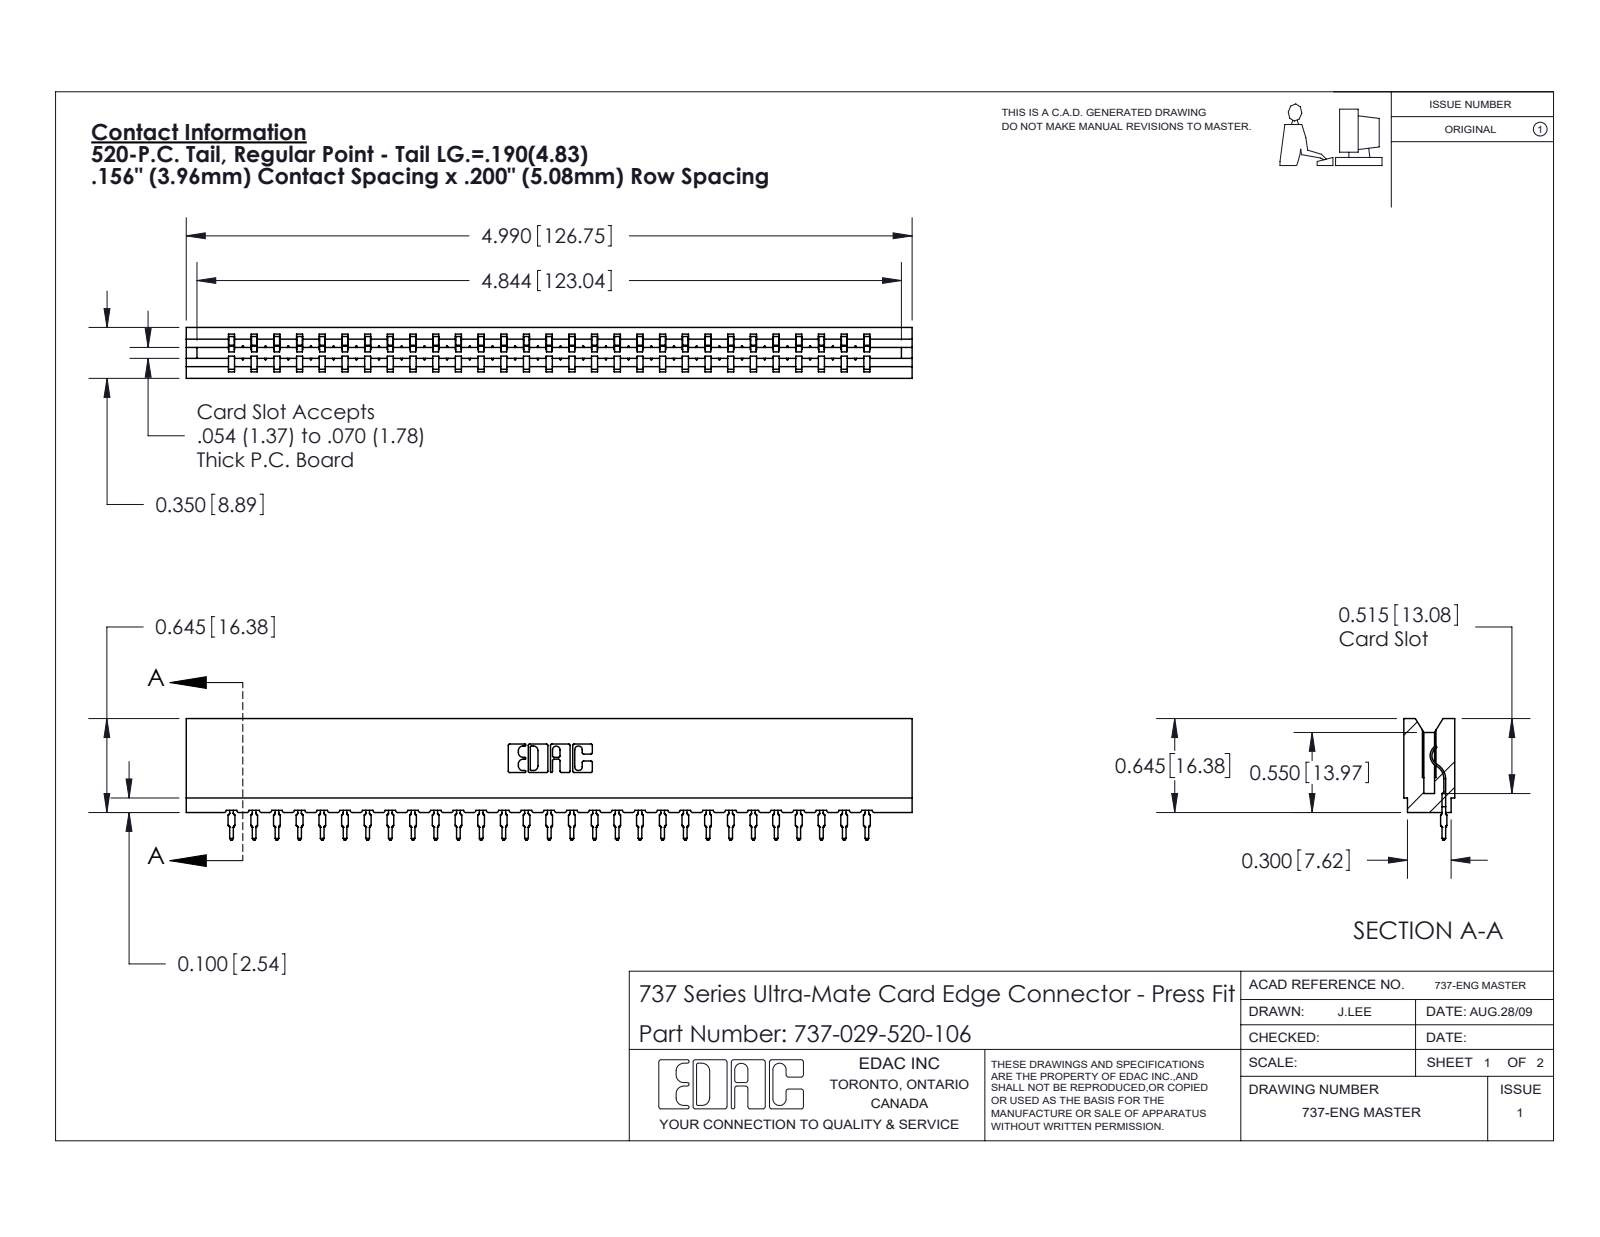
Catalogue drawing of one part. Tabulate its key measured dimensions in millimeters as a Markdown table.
| quantity | value |
| --- | --- |
| part name | 737 Part_Insulator Option - 06; 745-292-001_520; 737-029-520-106 |
| STEP written by | SolidWorks 2020 (CONFIG_CONTROL_DESIGN) |
| units | millimeters |
| bodies | 30 solids, 3372 faces (2027 planar, 591 cylindrical, 754 other) |
| overall size | 126.7 × 21.2 × 8.9 |
| volume | 12 300 mm³ |
| surface area | 16 070 mm² |
| partial cylindrical surfaces (radius × count) | 0.4 × 58, 0.5 × 58, 0.3 × 22, 0.2 × 6, 0.8 × 6, 0.1 × 4, 0.3 × 4, 0.7 × 3 |
| main face-to-face distances | 3.5, 5.4, 8.9, 1.9, 4, 15.8, 1.1, 7.7, 2.4, 4.2 |
